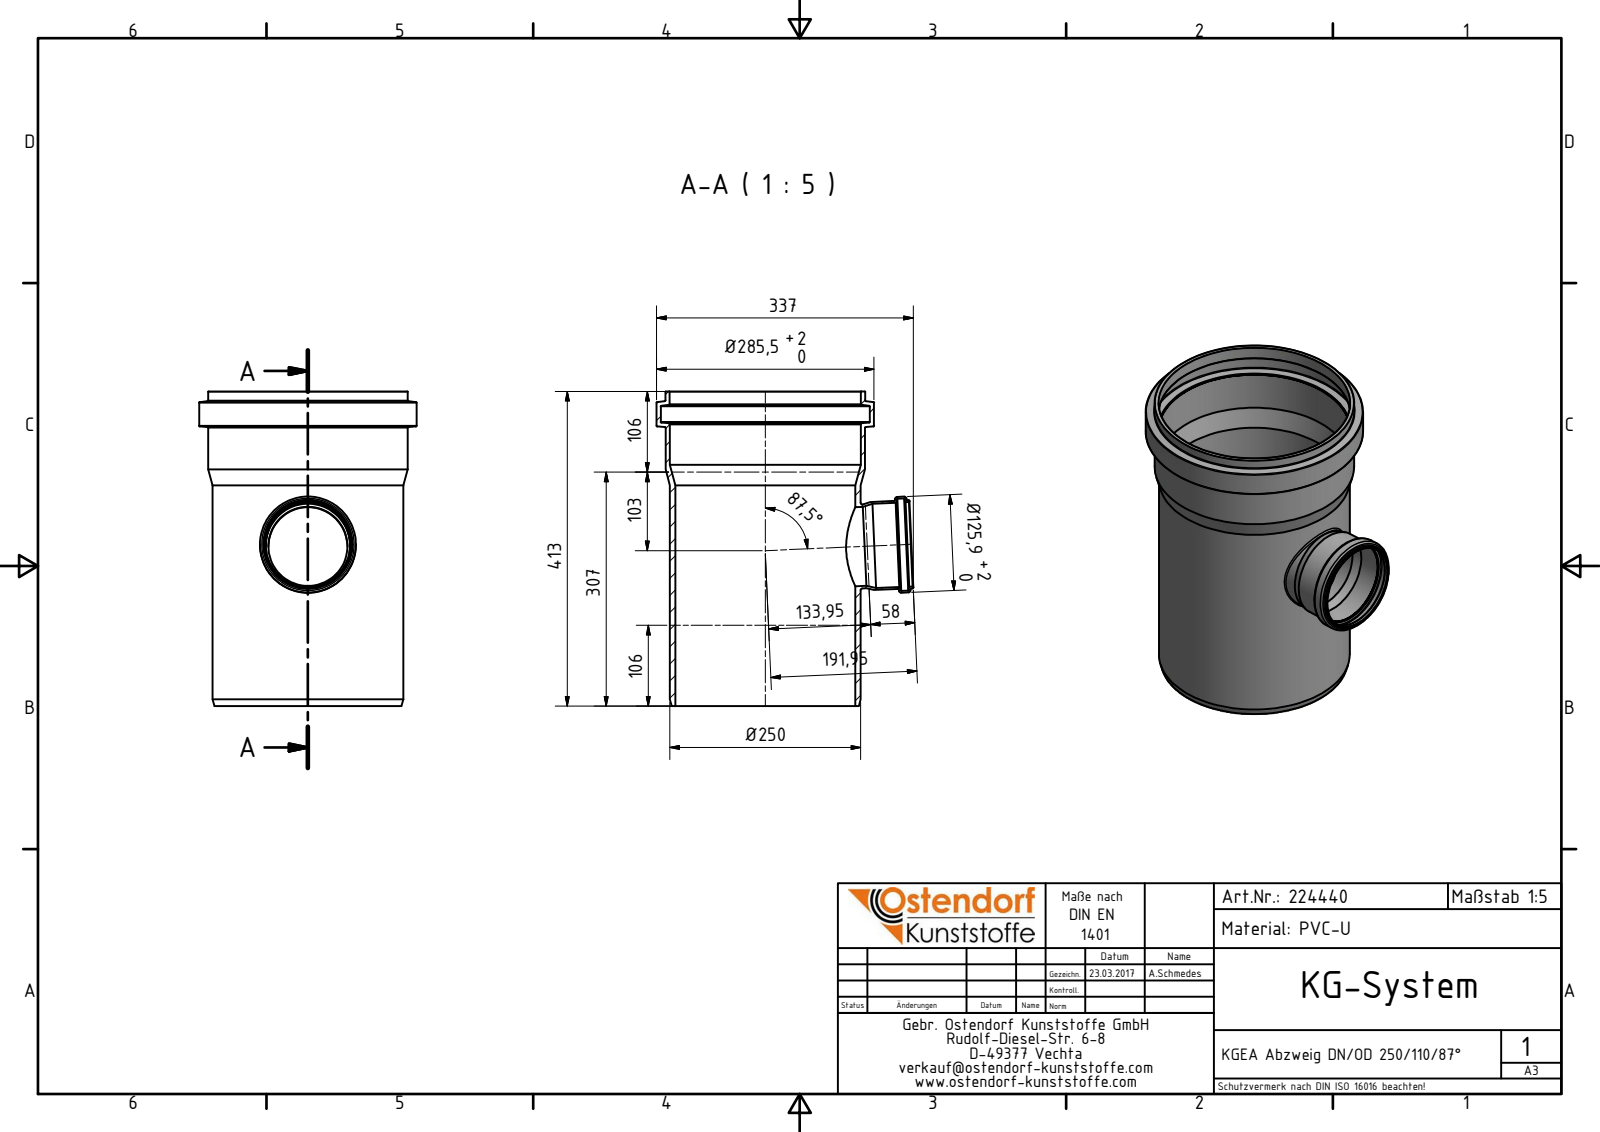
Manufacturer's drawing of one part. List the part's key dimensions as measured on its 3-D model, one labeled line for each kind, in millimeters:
Part name (STEP PRODUCT): 224440 KGEA Abzweig DN_OD 250_110_87°
STEP written by: Autodesk Inventor 2016 (AUTOMOTIVE_DESIGN)
Units: millimetres
Bodies: 1 solid, 57 faces (5 planar, 18 cylindrical, 34 other)
Overall size (bounding box): 413 × 337 × 285.5
Volume: 2 262 000 mm³ · Surface area: 729 375 mm²
Round holes (diameter × count): ⌀111 ×2, ⌀103.8 ×1, ⌀110.7 ×1, ⌀121.1 ×1, ⌀236.3 ×1, ⌀250.8 ×1, ⌀251.1 ×1, ⌀274.5 ×1
Round bosses / shafts (diameter × count): ⌀285.5 ×1, ⌀262.1 ×1, ⌀261.8 ×1, ⌀250.5 ×1, ⌀125.9 ×1, ⌀115.8 ×1, ⌀115.5 ×1, ⌀110.2 ×1
Main face-to-face distances: 413, 369.77, 43.23, 18.2
